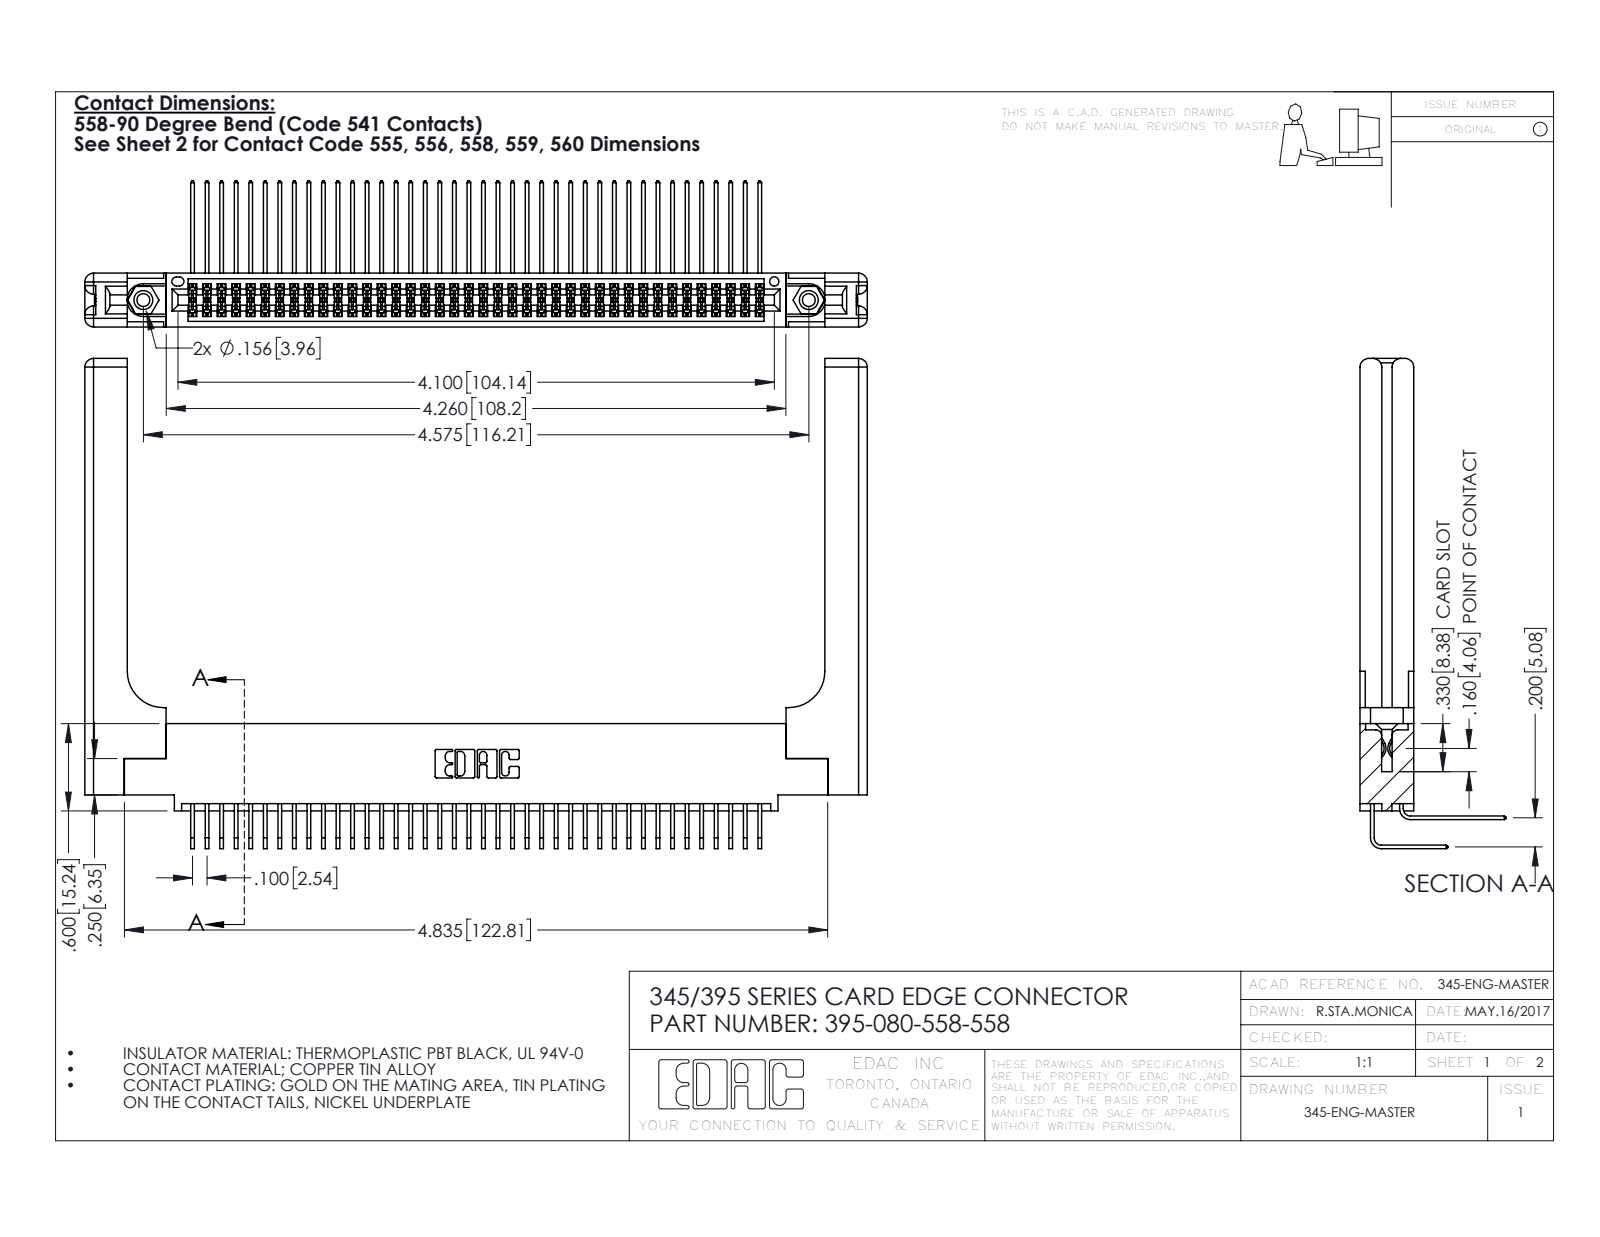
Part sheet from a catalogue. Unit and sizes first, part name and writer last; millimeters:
Units: millimetres
Overall size (bounding box): 136.6 × 85.6 × 25.5
Round holes (diameter × count): ⌀2.3 ×2, ⌀3.2 ×2, ⌀4 ×2, ⌀1.6 ×1
Round bosses / shafts (diameter × count): ⌀3.9 ×2
Partial cylindrical surfaces — rounded edges, fillets, slot ends (radius × count): R0.2 ×121, R0.3 ×22, R1.5 ×16, R0.2 ×6, R0.8 ×6, R0.7 ×3, R0.4 ×2, R0.5 ×2
Main face-to-face distances: 1.8, 9.4, 7.6, 5.1, 2.5, 6.9, 0.6, 5.7, 3.8, 3.8
Hole centre spacings: 6.9, 110.2, 116.2
Volume: 22 120 mm³ · Surface area: 27 450 mm²
Bodies: 85 solids, 4546 faces (3032 planar, 1454 cylindrical, 60 other)
Part name (STEP PRODUCT): 345-250-001_345-250-001-102; 395-080-558-558; 345-220-058_345-220-058; 345-292-001_558 Tail - 2 (+2 more)
STEP written by: SolidWorks 2016 (CONFIG_CONTROL_DESIGN)
